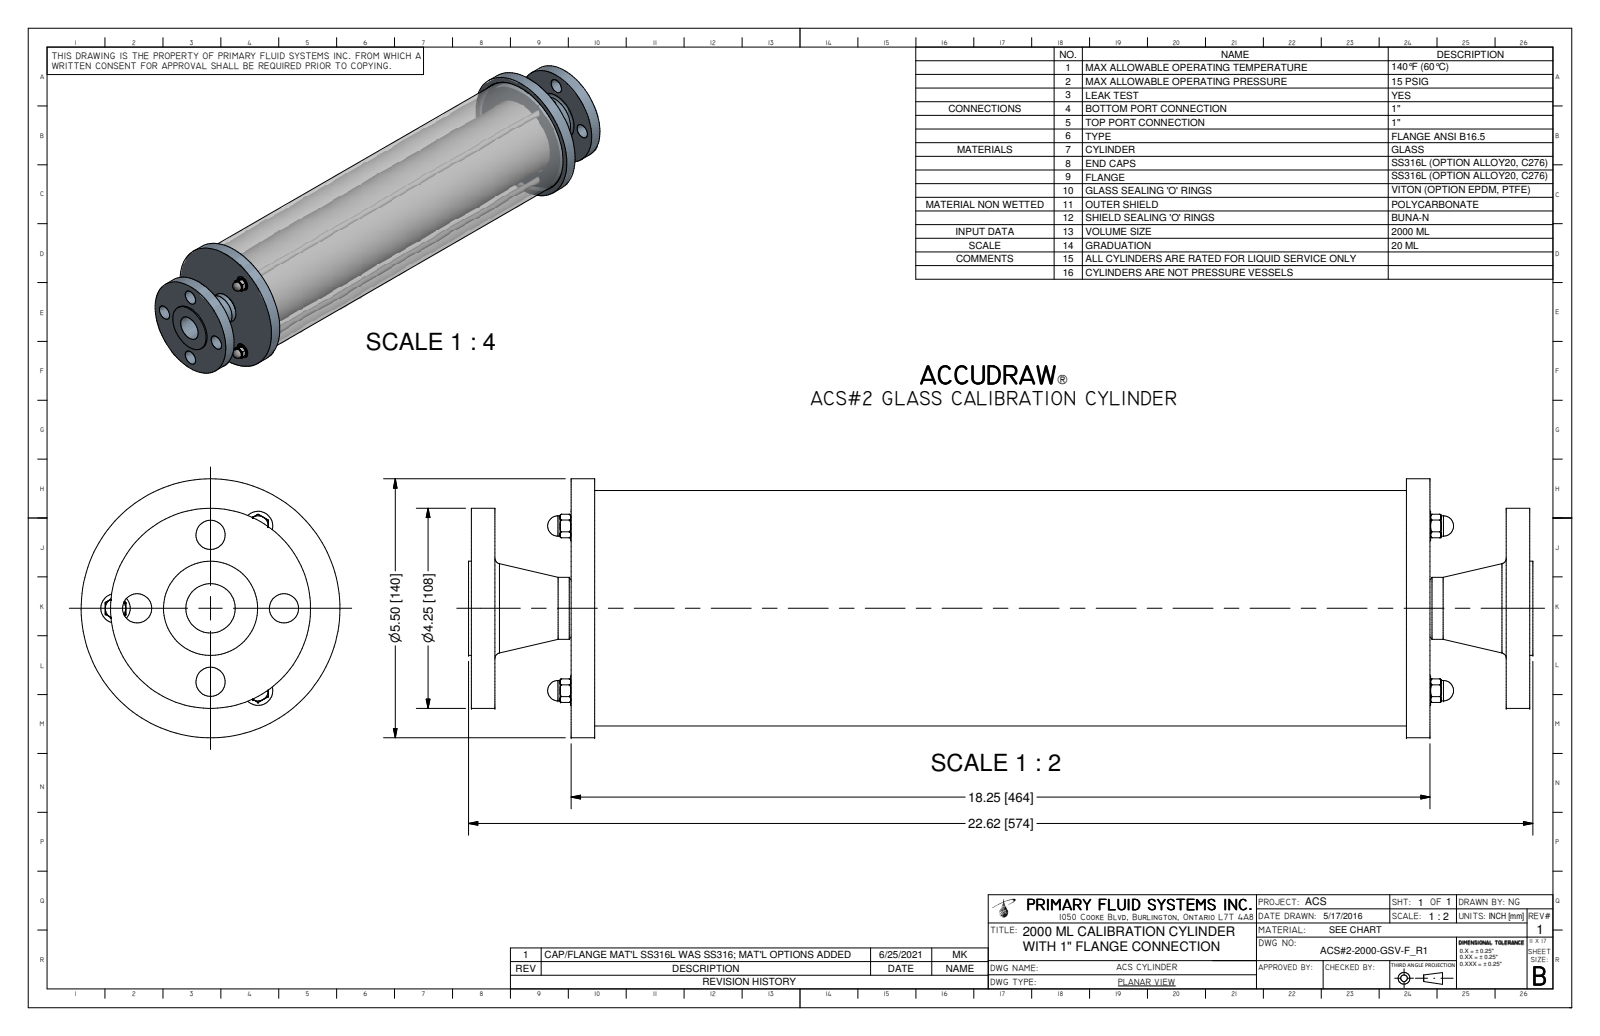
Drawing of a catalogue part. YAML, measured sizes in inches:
part_name: "ACS#2-2000-GSV-F_R0; ACS-3-2000-METAL-S_R1; ACS-2-2000-PC_R6; ACS-1-2000-A_R0 (+4 more)"
step_written_by: "Autodesk Inventor 2009 (AUTOMOTIVE_DESIGN)"
units: inches
bodies: {solids: 21, faces: 455, planar: 46, cylindrical: 57, other: 352}
overall_size: [22.615, 5.5, 5.5]
volume: 90.29
surface_area: 1202
round_holes:
  - {diameter: 0.62, count: 4}
  - {diameter: 0.18, count: 3}
  - {diameter: 0.266, count: 3}
  - {diameter: 0.281, count: 3}
  - {diameter: 1.049, count: 1}
  - {diameter: 3.15, count: 1}
  - {diameter: 3.4, count: 1}
  - {diameter: 4.75, count: 1}
  - {diameter: 5.05, count: 1}
round_bosses_or_shafts:
  - {diameter: 0.625, count: 3}
  - {diameter: 0.25, count: 3}
  - {diameter: 5.5, count: 1}
  - {diameter: 5, count: 1}
  - {diameter: 4.7, count: 1}
  - {diameter: 4.25, count: 1}
  - {diameter: 3.346, count: 1}
  - {diameter: 3.1, count: 1}
face_to_face_distances: [0.5, 2.12, 19.87, 18.25, 17.75, 2.62, 20.37, 21.99, 1.62, 19.37]
hole_center_spacings: [1.56, 2.206, 2.019, 3.497, 1.027, 1.833, 2.551, 3.108]
